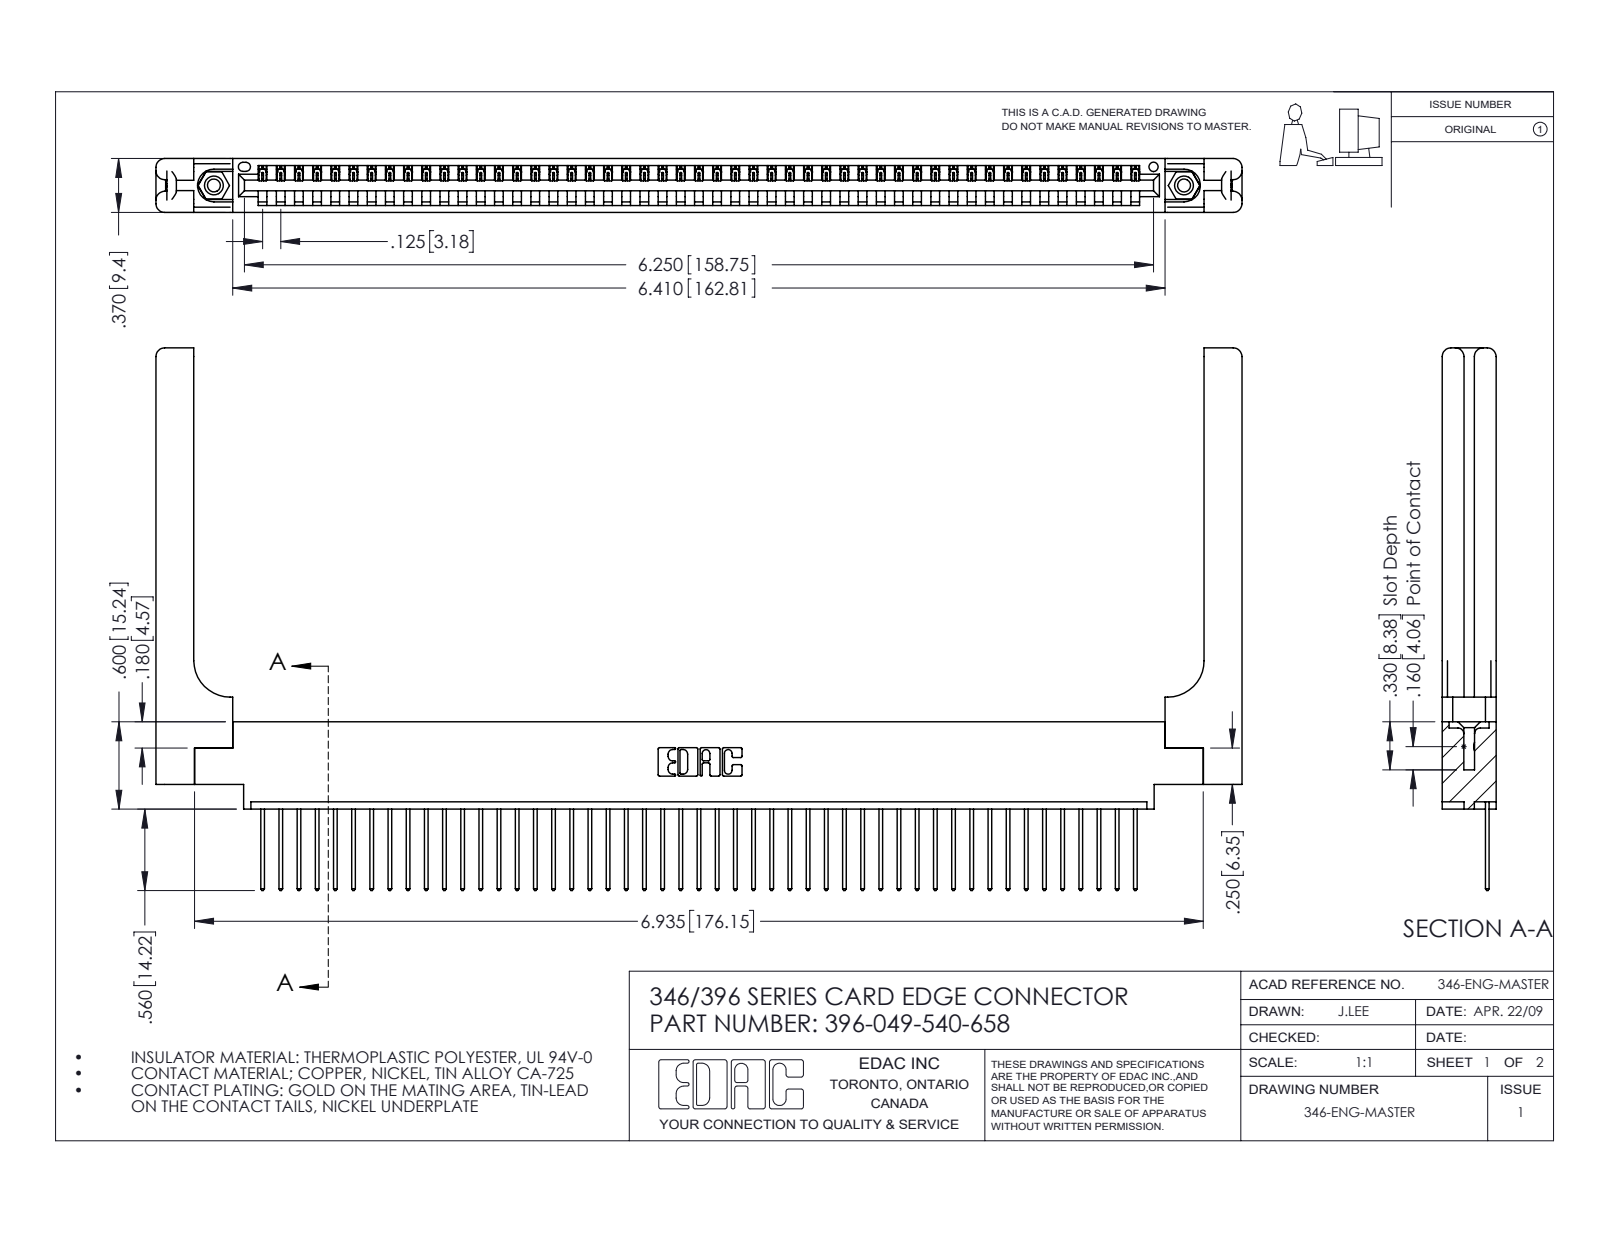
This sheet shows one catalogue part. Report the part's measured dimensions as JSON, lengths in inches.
{"part_name": "345-292-001_345-293-140; 346 Part_0.170 Offset - 0.156 Dia-TH; 345-250-001_345-250-001-102; 346-220-058_345-220-058 (+1 more)", "step_written_by": "SolidWorks 2016 (CONFIG_CONTROL_DESIGN)", "units": "inches", "bodies": {"solids": 54, "faces": 3224, "planar": 2188, "cylindrical": 976, "other": 60}, "overall_size": [7.466, 3.73, 0.37], "volume_in3": 1.564, "surface_area_in2": 44.22, "round_holes": [[0.089, 2], [0.125, 2], [0.156, 2], [0.064, 1]], "round_bosses_or_shafts": [[0.155, 2]], "partial_cylinders_radius": [[0.006, 98], [0.01, 98], [0.01, 22], [0.06, 16], [0.007, 6], [0.031, 6], [0.026, 3], [0.03, 2]], "face_to_face_distances": [0.37, 0.048, 0.322, 0.072, 0.148, 0.15, 0.25, 0.298, 0.025, 0.222], "hole_center_spacings": [0.246, 6.461, 6.67]}
